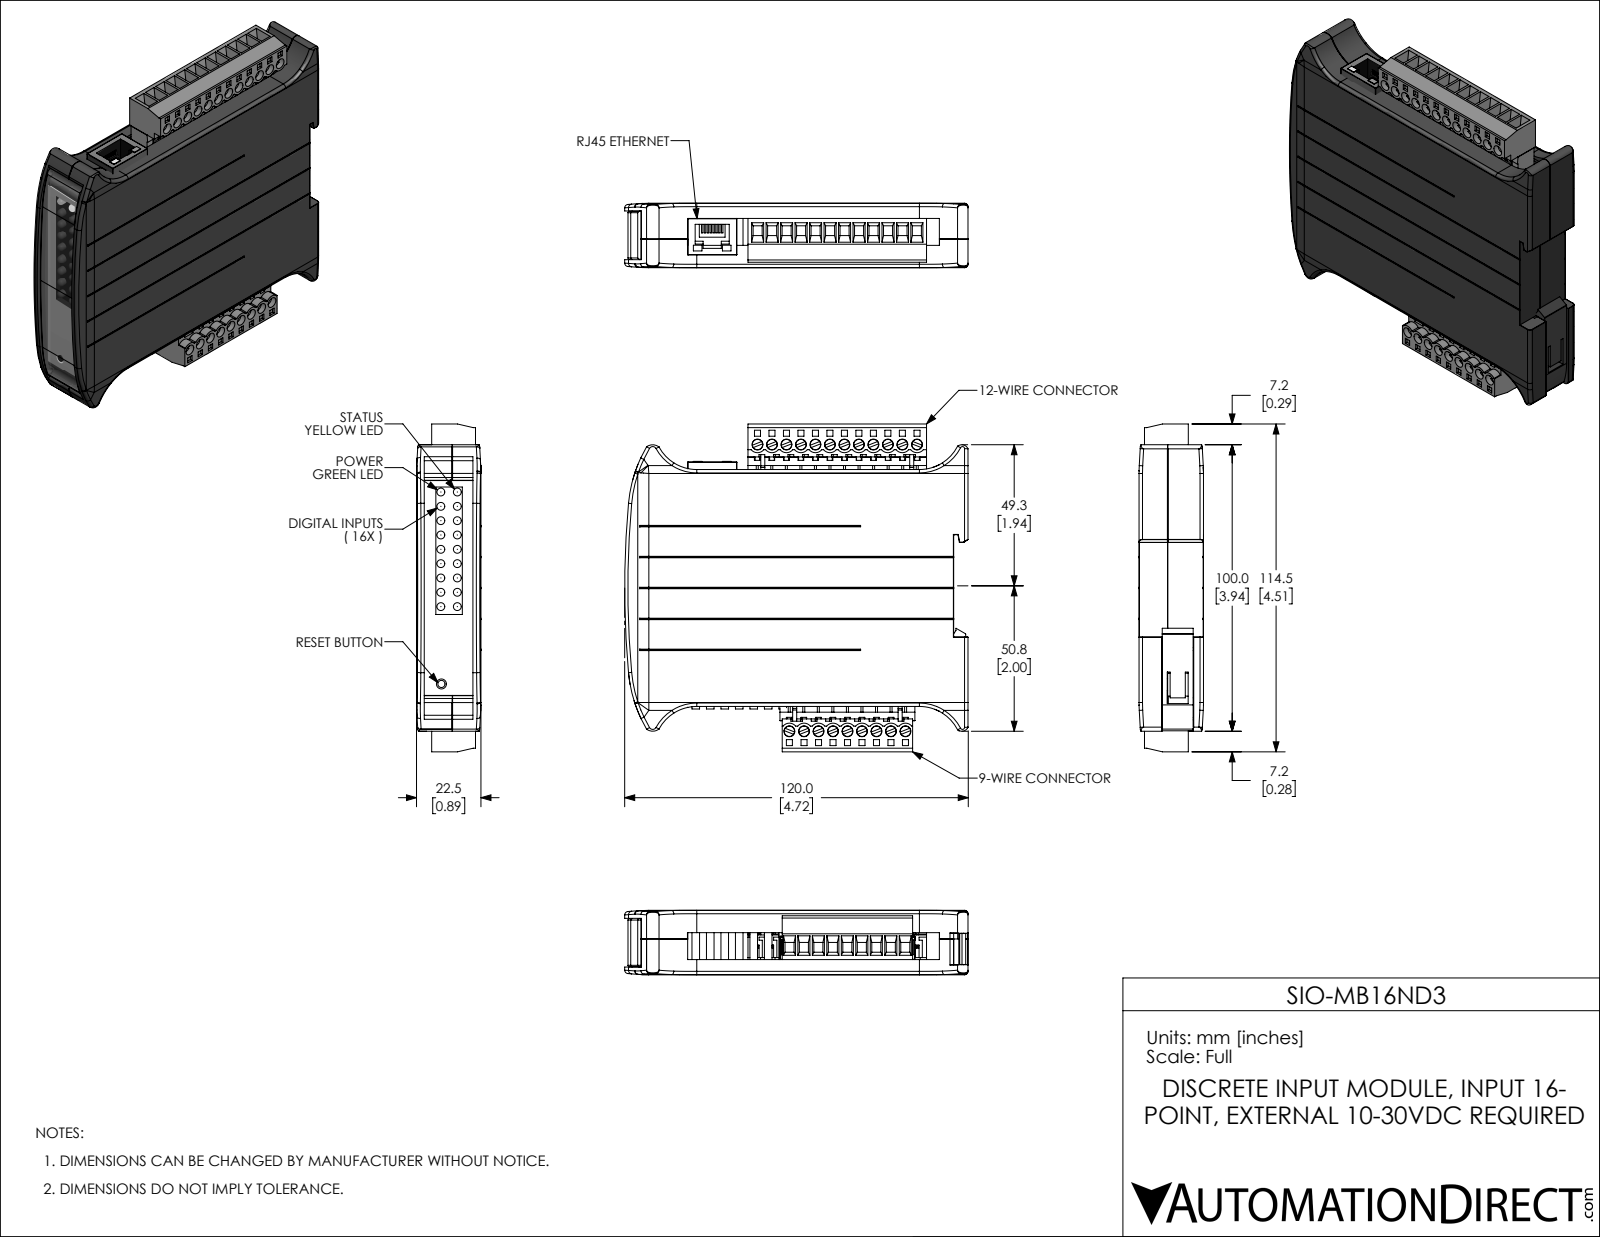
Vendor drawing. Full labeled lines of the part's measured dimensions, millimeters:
Part name (STEP PRODUCT): SIO-MB16ND3
STEP written by: SolidWorks 2019 (AUTOMOTIVE_DESIGN)
Units: millimetres
Bodies: 18 solids, 3177 faces (2422 planar, 495 cylindrical, 260 other)
Overall size (bounding box): 119.9 × 114.5 × 22.5
Volume: 82 920 mm³ · Surface area: 89 680 mm²
Round holes (diameter × count): ⌀3.8 ×21, ⌀2.4 ×2, ⌀3.5 ×1
Round bosses / shafts (diameter × count): ⌀3.6 ×21, ⌀2 ×21, ⌀2.7 ×18, ⌀3.9 ×1, ⌀2.5 ×1, ⌀2.3 ×1
Partial cylindrical surfaces — rounded edges, fillets, slot ends (radius × count): R0.1 ×122, R2.8 ×42, R2.9 ×21, R0.3 ×20, R1.2 ×12, R50.5 ×9, R0.1 ×8, R0.2 ×6
Main face-to-face distances: 1.5, 21, 22.5, 19.5, 15.7, 0.7, 7.2, 3.8, 5.3, 1.4
Hole centre spacings: 5.1, 10.1, 15.2, 20.2, 25.3, 100.1, 100.2, 100.7
